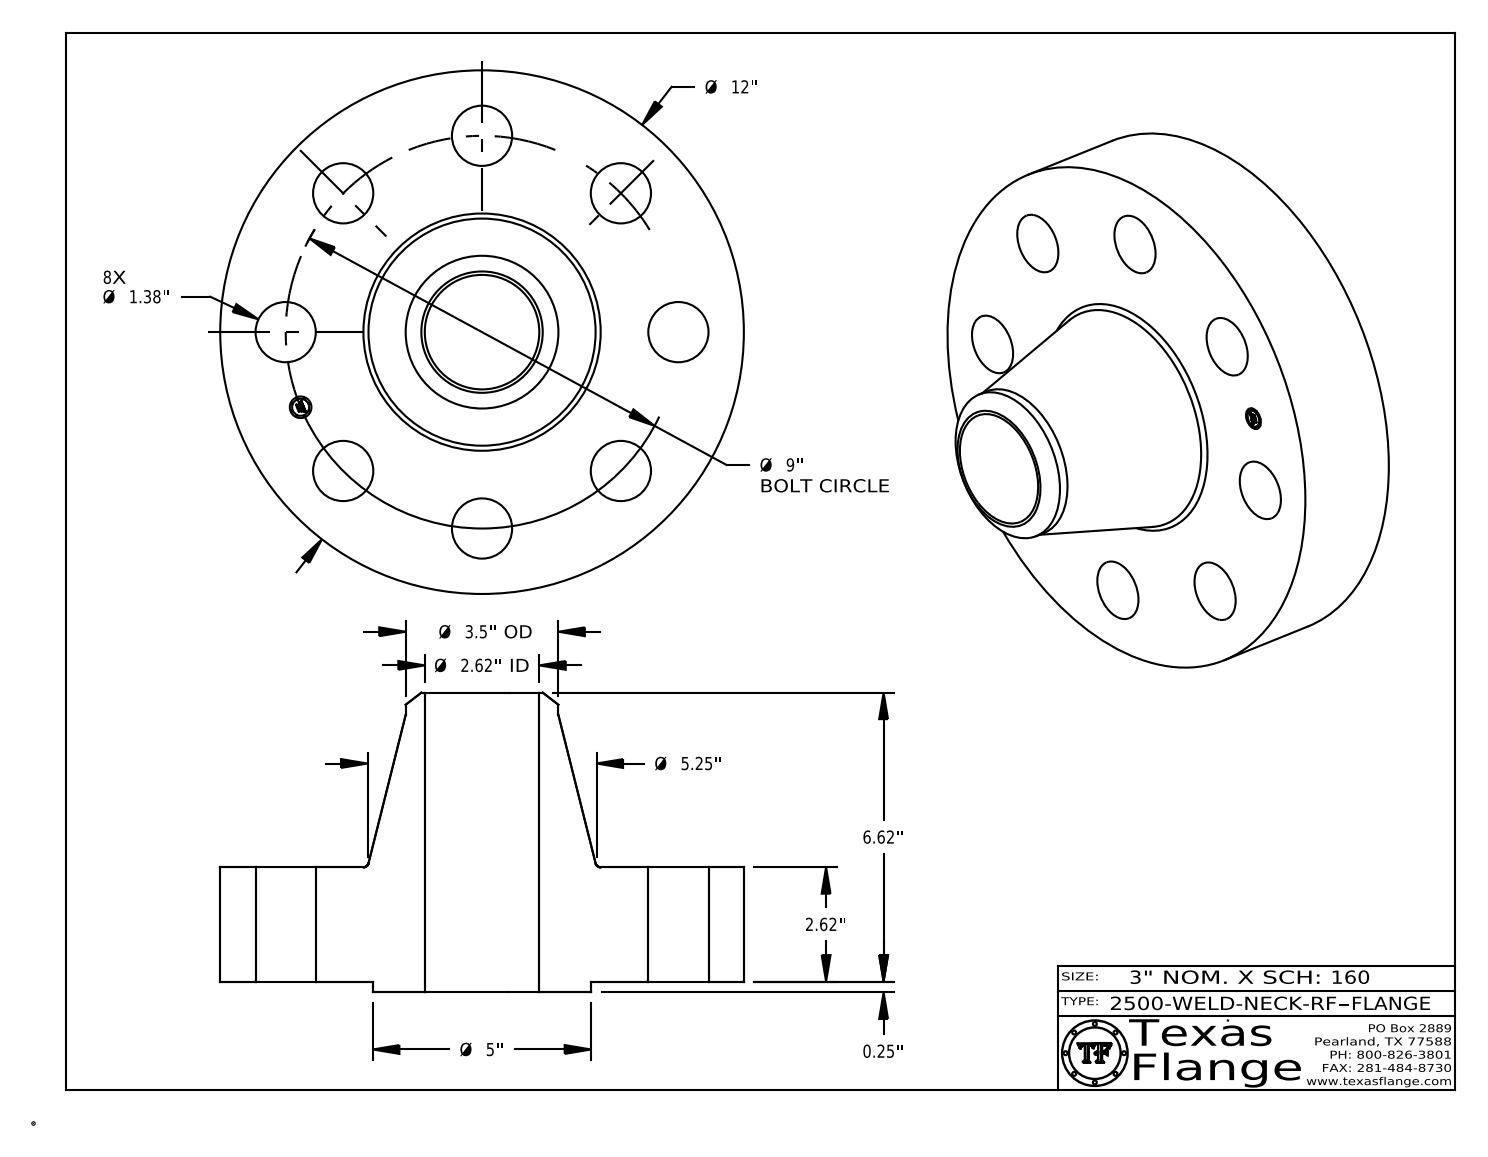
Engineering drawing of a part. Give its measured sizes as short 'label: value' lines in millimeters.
name: 2500-WELD-NECK-RF
written by: CATIA V5 STEP AP214 (AUTOMOTIVE_DESIGN)
unit: mm
bodies: 1 solid, 419 faces (369 planar, 44 cylindrical, 6 other)
size: 304.8 × 304.8 × 174.5
volume: 4 757 000 mm³; area: 311 100 mm²
holes: 8× ⌀35.1, 1× ⌀12.6, 1× ⌀66.6
bosses: 8× ⌀0.8, 1× ⌀304.8, 1× ⌀127, 1× ⌀88.9, 1× ⌀9.9
face distances: 66.5, 6.4, 72.9, 174.5, 168.1, 101.6, 72.5, 66.2, 0.4, 102
hole spacings: 114.3, 87.5, 161.6, 211.2, 44.6, 127, 190.1, 228.6
